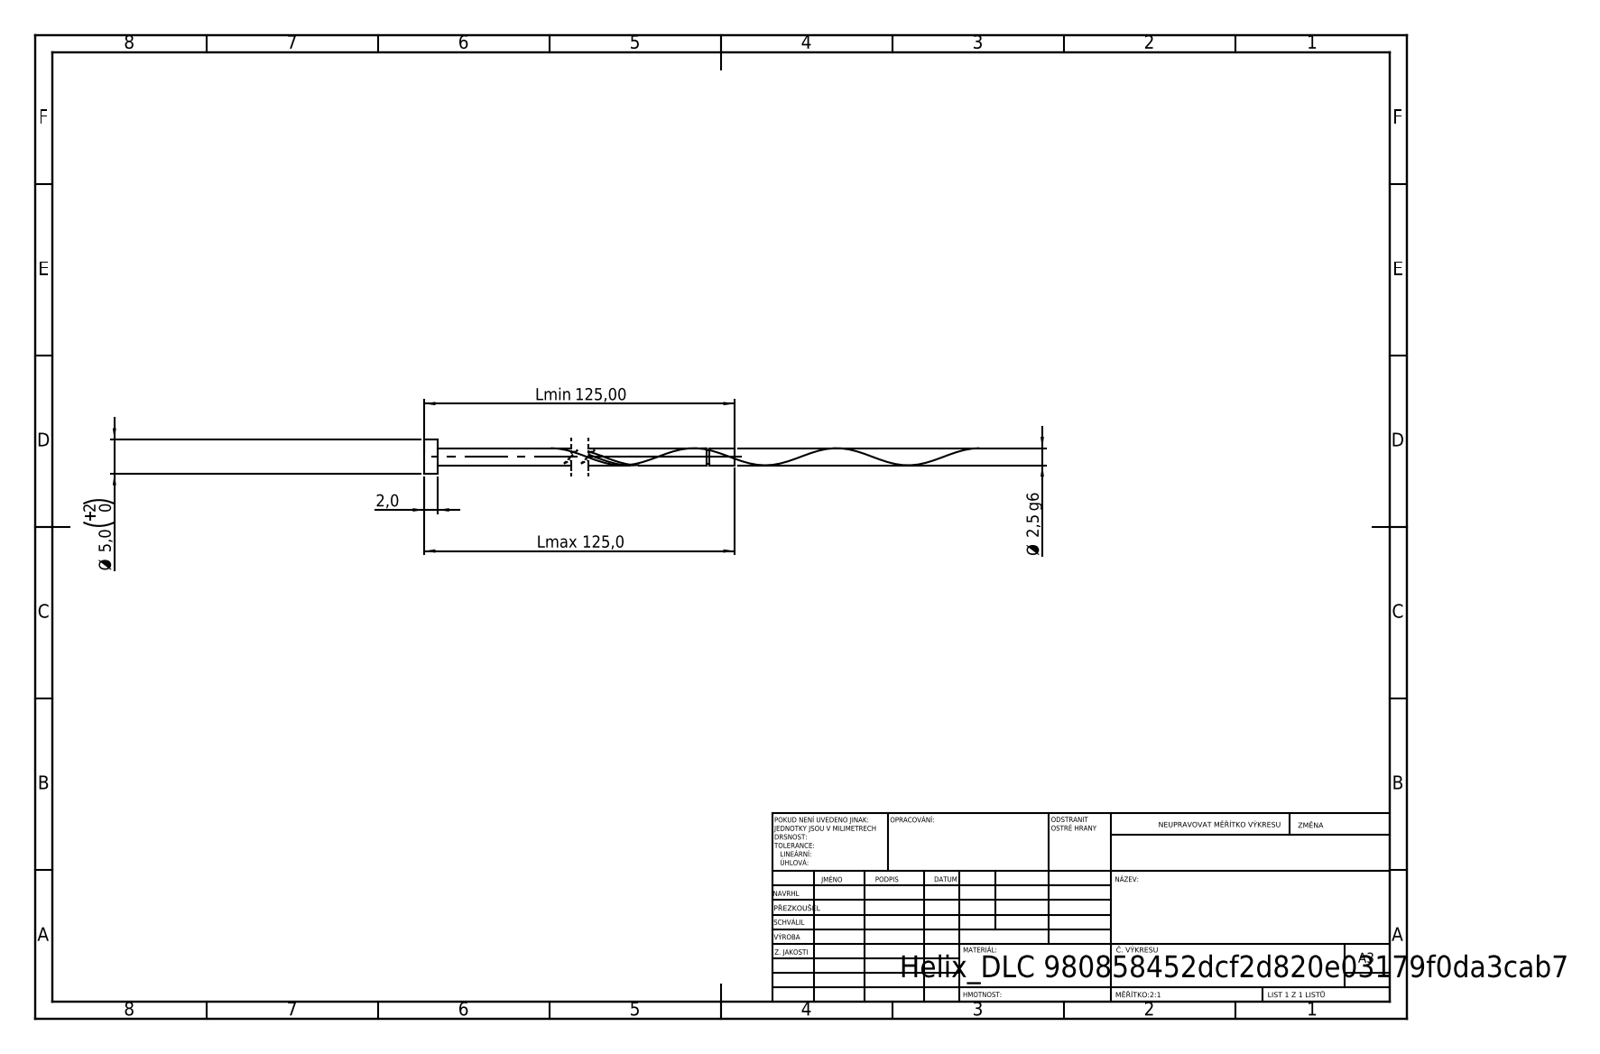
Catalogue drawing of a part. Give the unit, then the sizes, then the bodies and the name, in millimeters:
Units: millimetres
Overall size (bounding box): 125 × 5 × 5
Round bosses / shafts (diameter × count): ⌀5 ×1, ⌀2.5 ×1, ⌀2 ×1
Main face-to-face distances: 2, 125, 123, 121.34, 119.34, 3.66, 120.84, 118.84, 0.5, 4.16
Volume: 636 mm³ · Surface area: 1 056 mm²
Bodies: 1 solid, 21 faces (6 planar, 14 cylindrical, 1 other)
STEP written by: SolidWorks 2019 (CONFIG_CONTROL_DESIGN)
